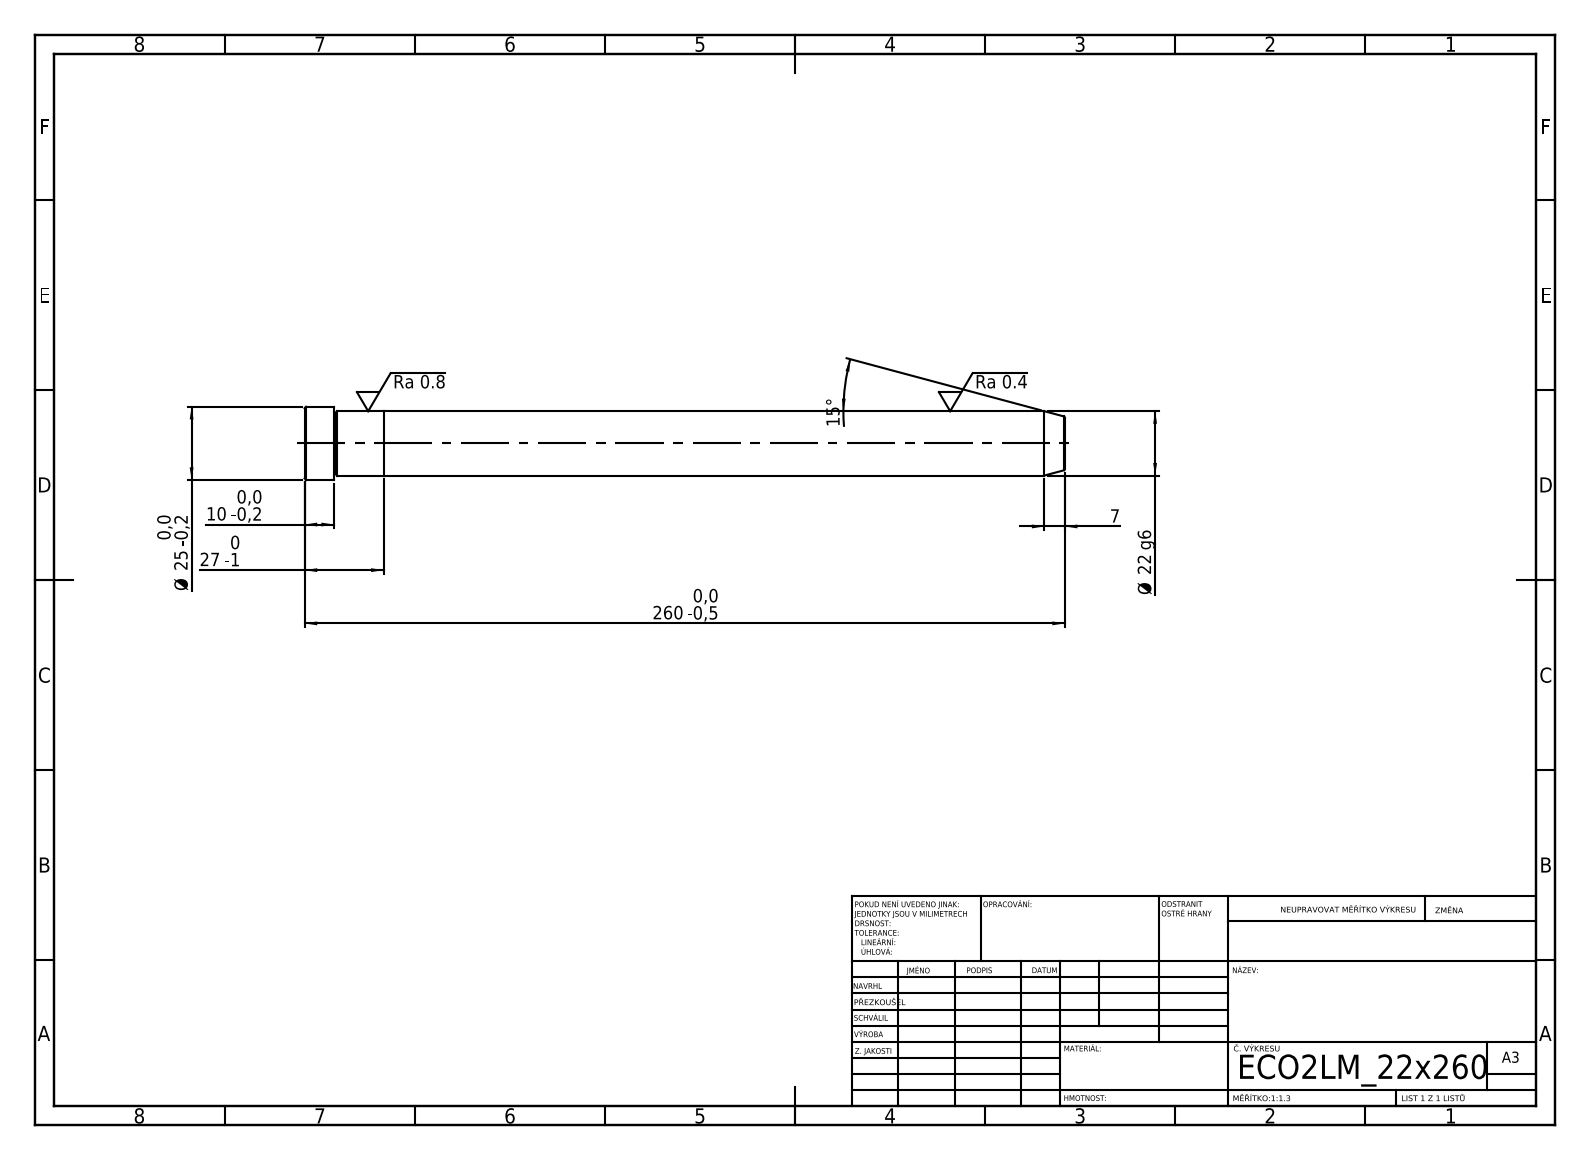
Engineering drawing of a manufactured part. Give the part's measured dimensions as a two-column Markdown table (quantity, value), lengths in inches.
| quantity | value |
| --- | --- |
| STEP written by | SolidWorks 2019 (CONFIG_CONTROL_DESIGN) |
| units | inches |
| bodies | 2 solids, 21 faces (5 planar, 6 cylindrical, 10 other) |
| overall size | 10.236 × 0.984 × 0.984 |
| volume | 6.07 in³ |
| surface area | 30.49 in² |
| round bosses / shafts (diameter × count) | 0.984 × 1, 0.866 × 1 |
| main face-to-face distances | 1.063, 9.173, 10.236, 9.843, 0.669, 0.394 |
